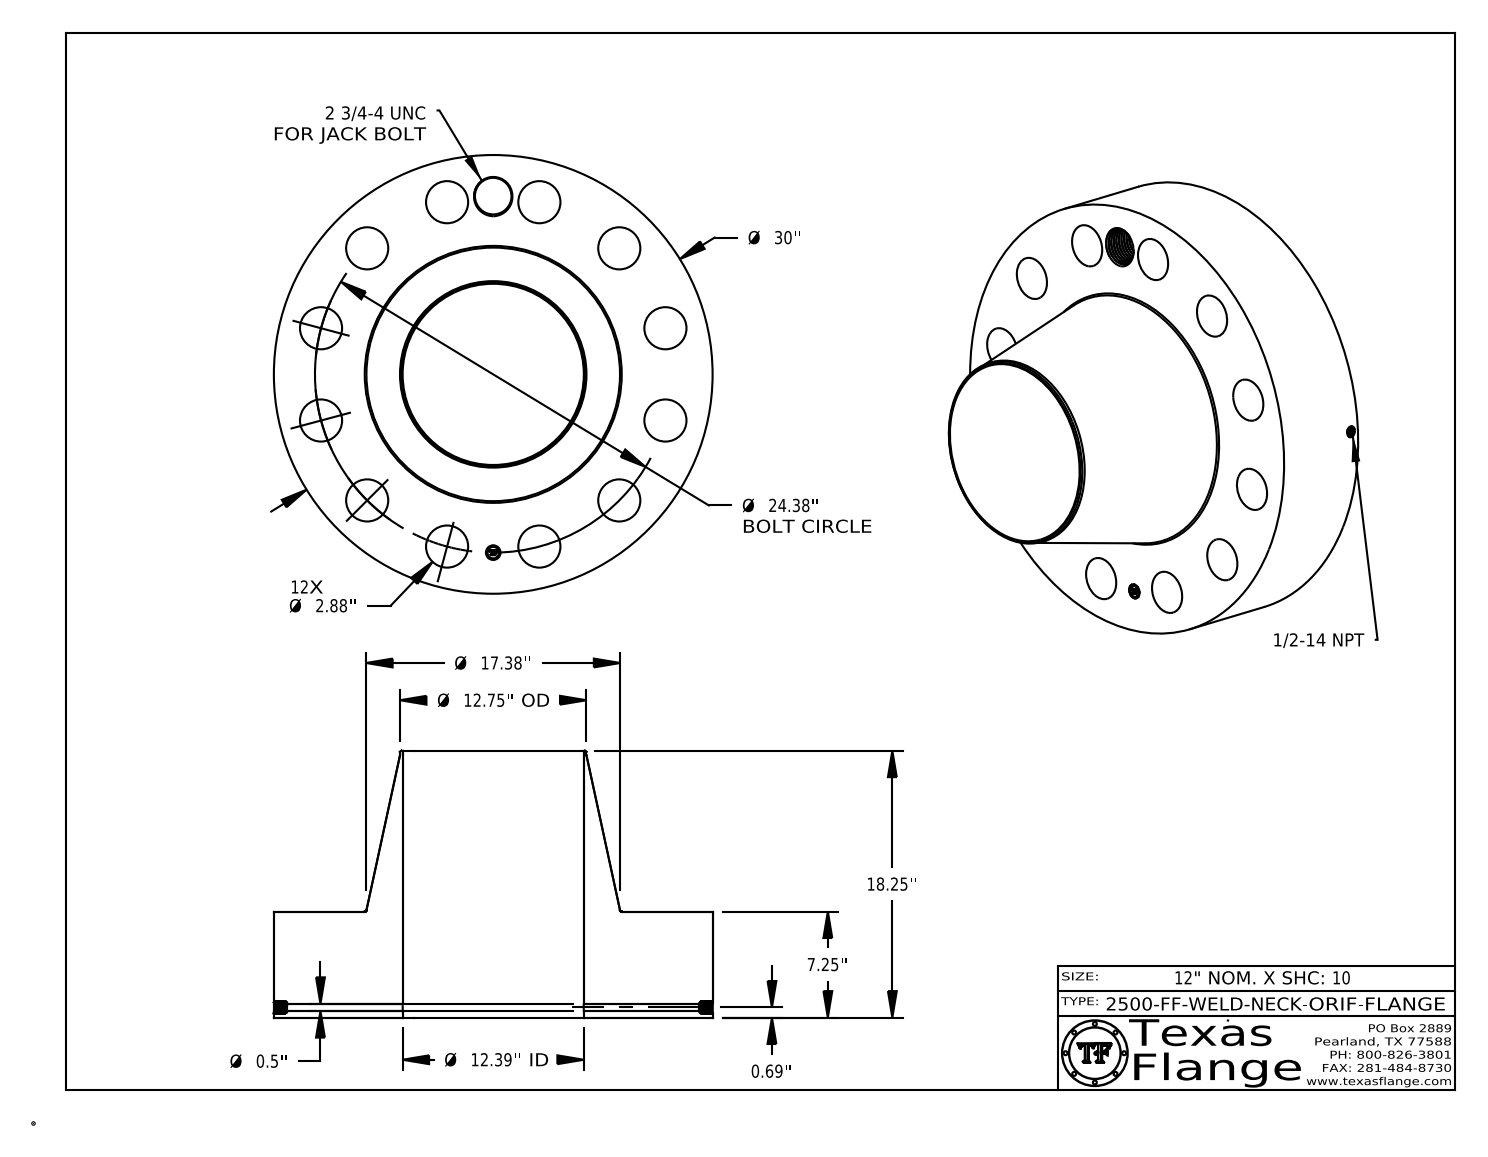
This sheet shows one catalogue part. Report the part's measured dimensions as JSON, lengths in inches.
{"part_name": "2500-FF-WELD-NECK", "step_written_by": "CATIA V5 STEP AP214 (AUTOMOTIVE_DESIGN)", "units": "inches", "bodies": {"solids": 1, "faces": 858, "planar": 368, "cylindrical": 128, "other": 362}, "overall_size": [30, 30, 18.25], "volume_in3": 4274, "surface_area_in2": 3719, "round_holes": [[2.88, 12], [0.5, 1], [0.672, 1], [1, 1], [2.5, 1], [12.39, 1]], "round_bosses_or_shafts": [[0.061, 8], [30, 1], [12.75, 1], [0.788, 1]], "face_to_face_distances": [7.25, 18.25, 11, 0.015, 7.235, 11.015, 0.298, 0.292, 0.054, 0.248], "hole_center_spacings": [12.19, 17.239, 23.55, 6.31, 21.114, 24.38, 3.182, 6.31]}
